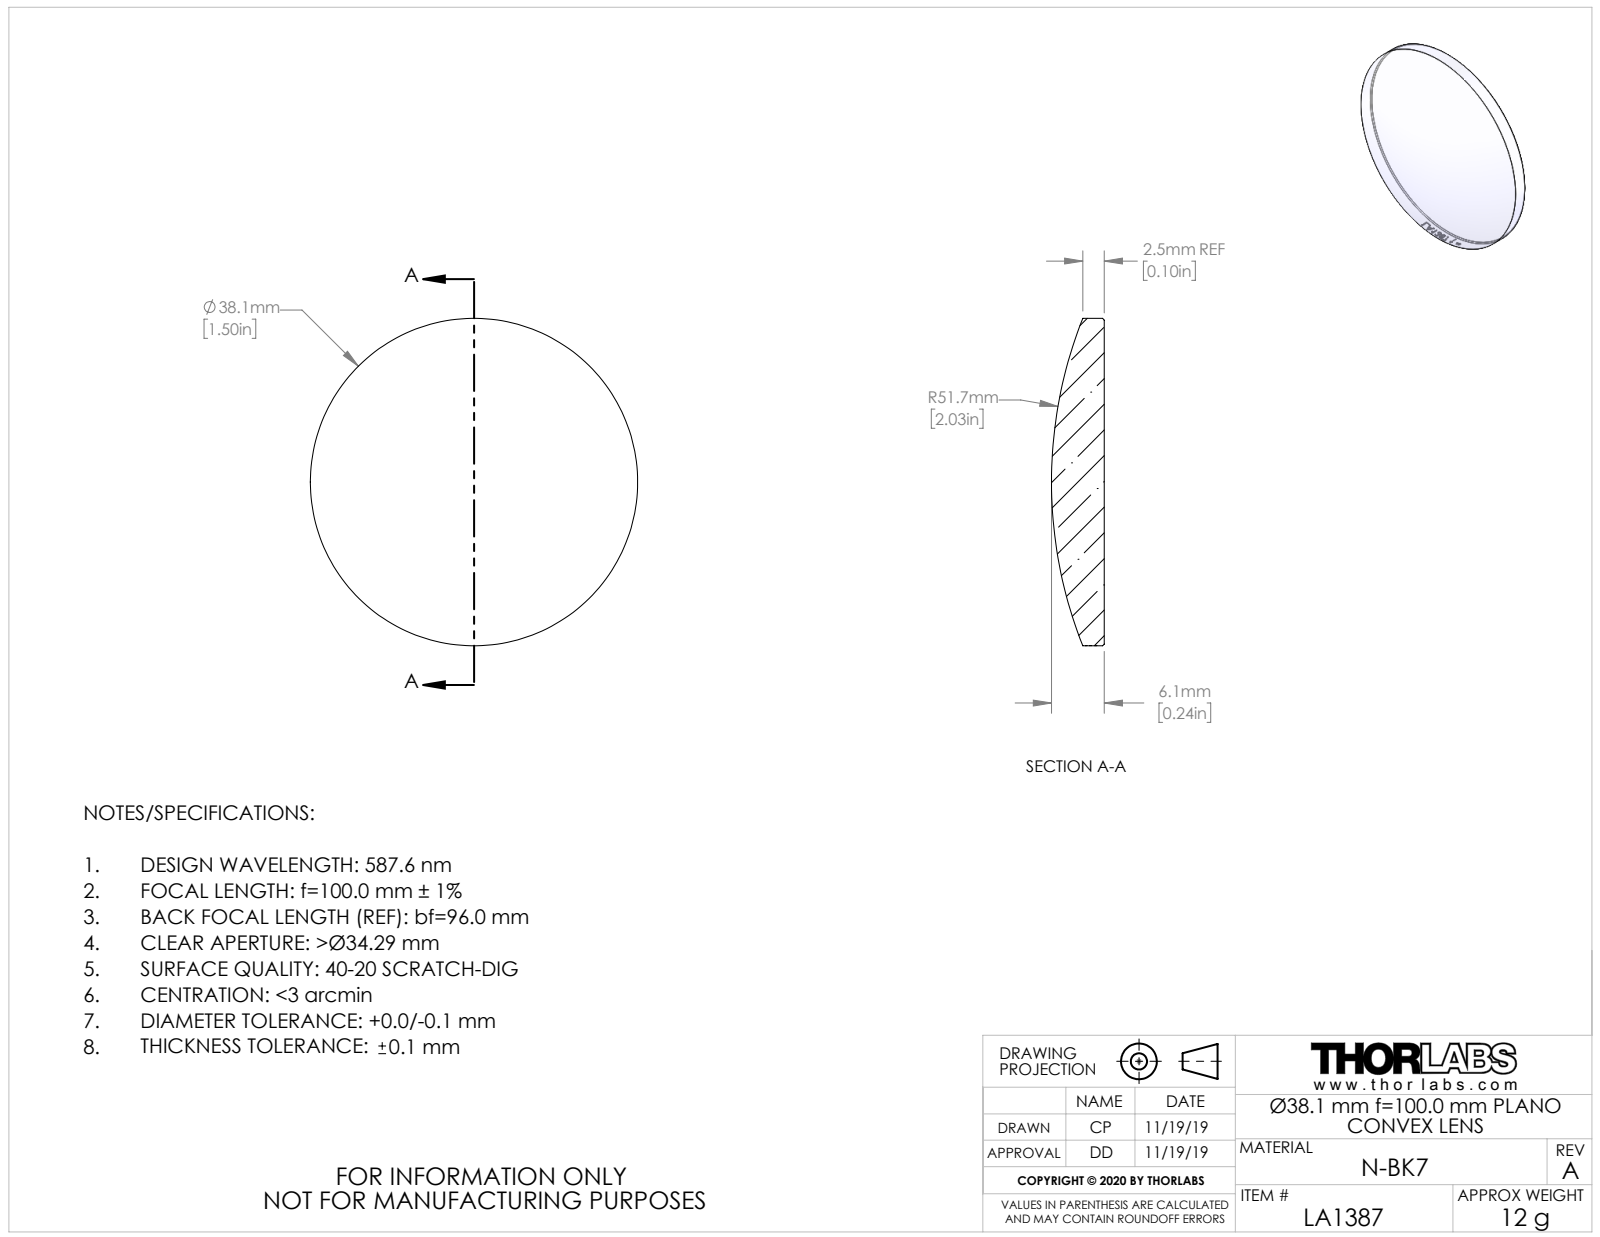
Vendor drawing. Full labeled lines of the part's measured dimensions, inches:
Part name (STEP PRODUCT): TTN200654-E0W
STEP written by: SolidWorks 2018 (CONFIG_CONTROL_DESIGN)
Units: inches
Bodies: 1 solid, 20 faces (1 planar, 15 cylindrical, 4 other)
Overall size (bounding box): 1.5 × 1.5 × 0.242
Volume: 0.302 in³ · Surface area: 4.041 in²
Round bosses / shafts (diameter × count): ⌀1.5 ×1
